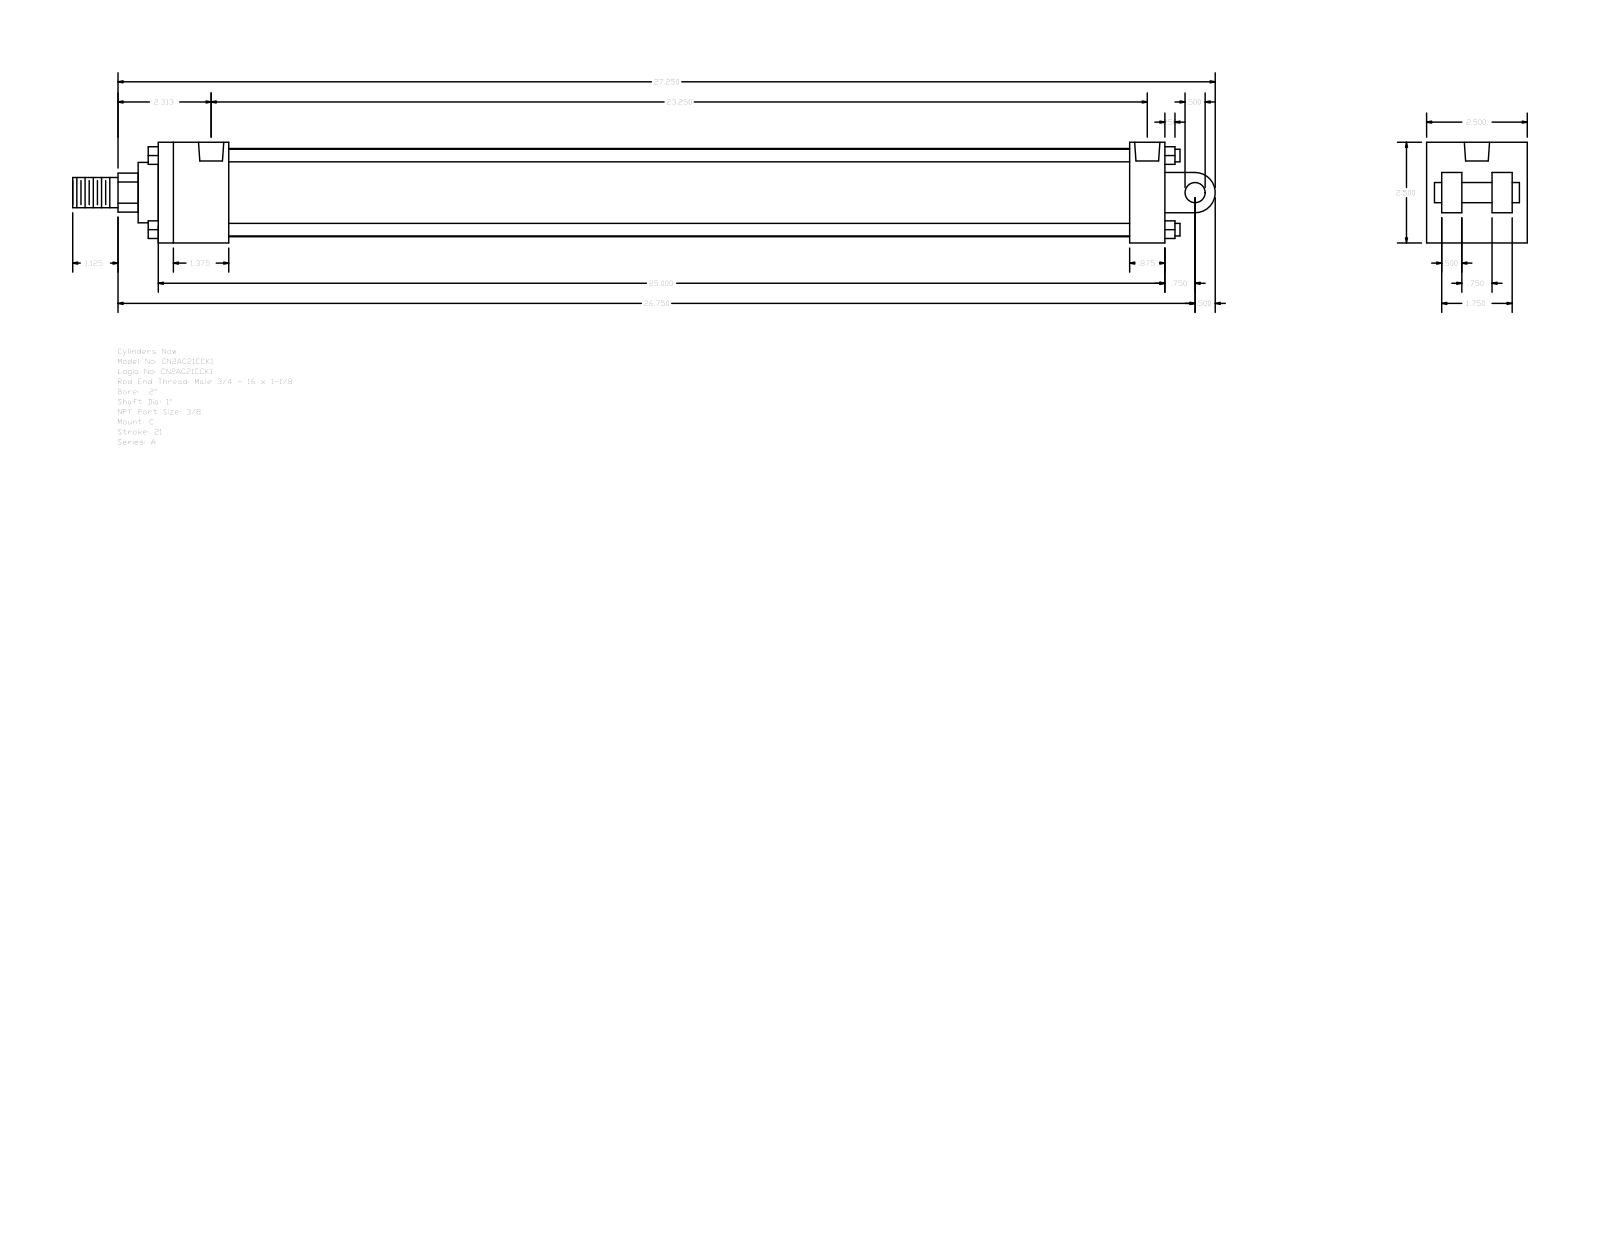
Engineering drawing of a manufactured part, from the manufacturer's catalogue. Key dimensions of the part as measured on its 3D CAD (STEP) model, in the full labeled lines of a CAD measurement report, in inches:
Part name (STEP PRODUCT): A_C__0200_1
STEP written by: GSSL Pune (CONFIG_CONTROL_DESIGN)
Units: inches
Bodies: 0 solids, 135 faces (102 planar, 33 cylindrical, 0 other)
Overall size (bounding box): 28.375 × 2.5 × 2.5
Round holes (diameter × count): ⌀0.219 ×4, ⌀0.627 ×2
Round bosses / shafts (diameter × count): ⌀0.313 ×4, ⌀2.19 ×1, ⌀1.5 ×1, ⌀1 ×1, ⌀0.75 ×1, ⌀0.5 ×1
Partial cylindrical surfaces — rounded edges, fillets, slot ends (radius × count): R0.484 ×1, R0.5 ×1
Main face-to-face distances: 2.5, 25, 1.75, 0.5, 0.375, 23.25, 24.125, 22.375, 0.875, 2.125
Hole centre spacings: 23.031, 0.063, 0.157, 23.093, 23.187, 23.25
